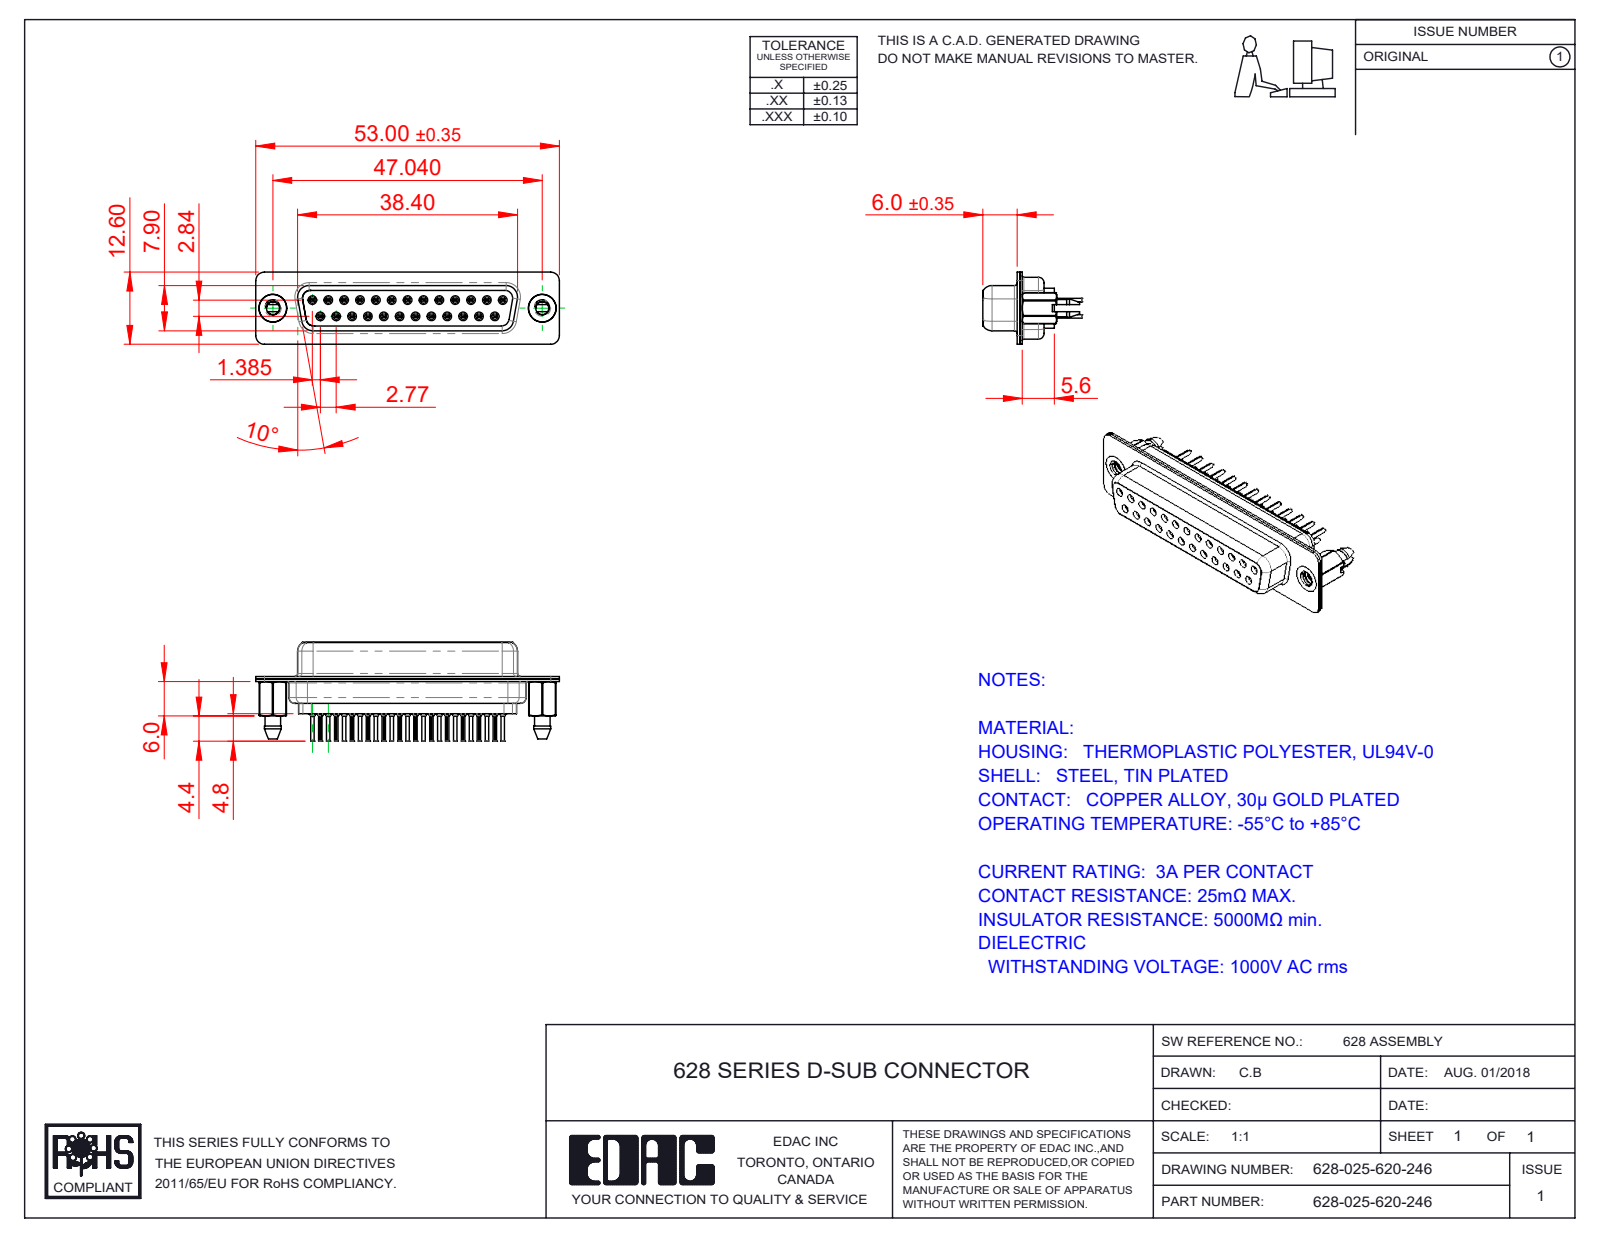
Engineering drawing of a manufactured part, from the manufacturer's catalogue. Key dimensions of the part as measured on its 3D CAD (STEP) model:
Part name (STEP PRODUCT): 628 Shell Rear_25 Contacts; 628 4-40 Threaded Boardlock_LP; 628 Contact Row 2_20L; 628-025-620-246 (+3 more)
STEP written by: SolidWorks 2020 (CONFIG_CONTROL_DESIGN)
Units: millimetres
Bodies: 30 solids, 3528 faces (874 planar, 994 cylindrical, 1660 other)
Overall size (bounding box): 53 × 17.3 × 12.6
Volume: 3 951 mm³ · Surface area: 9 635 mm²
Round holes (diameter × count): ⌀0.2 ×25, ⌀0.8 ×25, ⌀0.9 ×25, ⌀1.1 ×25, ⌀1.6 ×25, ⌀1.7 ×13, ⌀2.26 ×2, ⌀4 ×2, ⌀4.05 ×2, ⌀4.85 ×2
Round bosses / shafts (diameter × count): ⌀2 ×25, ⌀1.5 ×25, ⌀1.2 ×25, ⌀0.6 ×25, ⌀4.95 ×2, ⌀4.8 ×2
Partial cylindrical surfaces — rounded edges, fillets, slot ends (radius × count): R0.1 ×50, R0.28 ×25, R1.5 ×18, R2 ×12, R1.35 ×6, R1.6 ×6, R0.25 ×4, R0.5 ×4
Main face-to-face distances: 0.45, 0.4, 6.6, 1.9, 8.5, 0.9, 1.4, 7.05, 0.85, 7.45
Hole centre spacings: 3.16, 8.31, 2.77, 5.54, 11.08, 16.62, 5.03, 5.04
